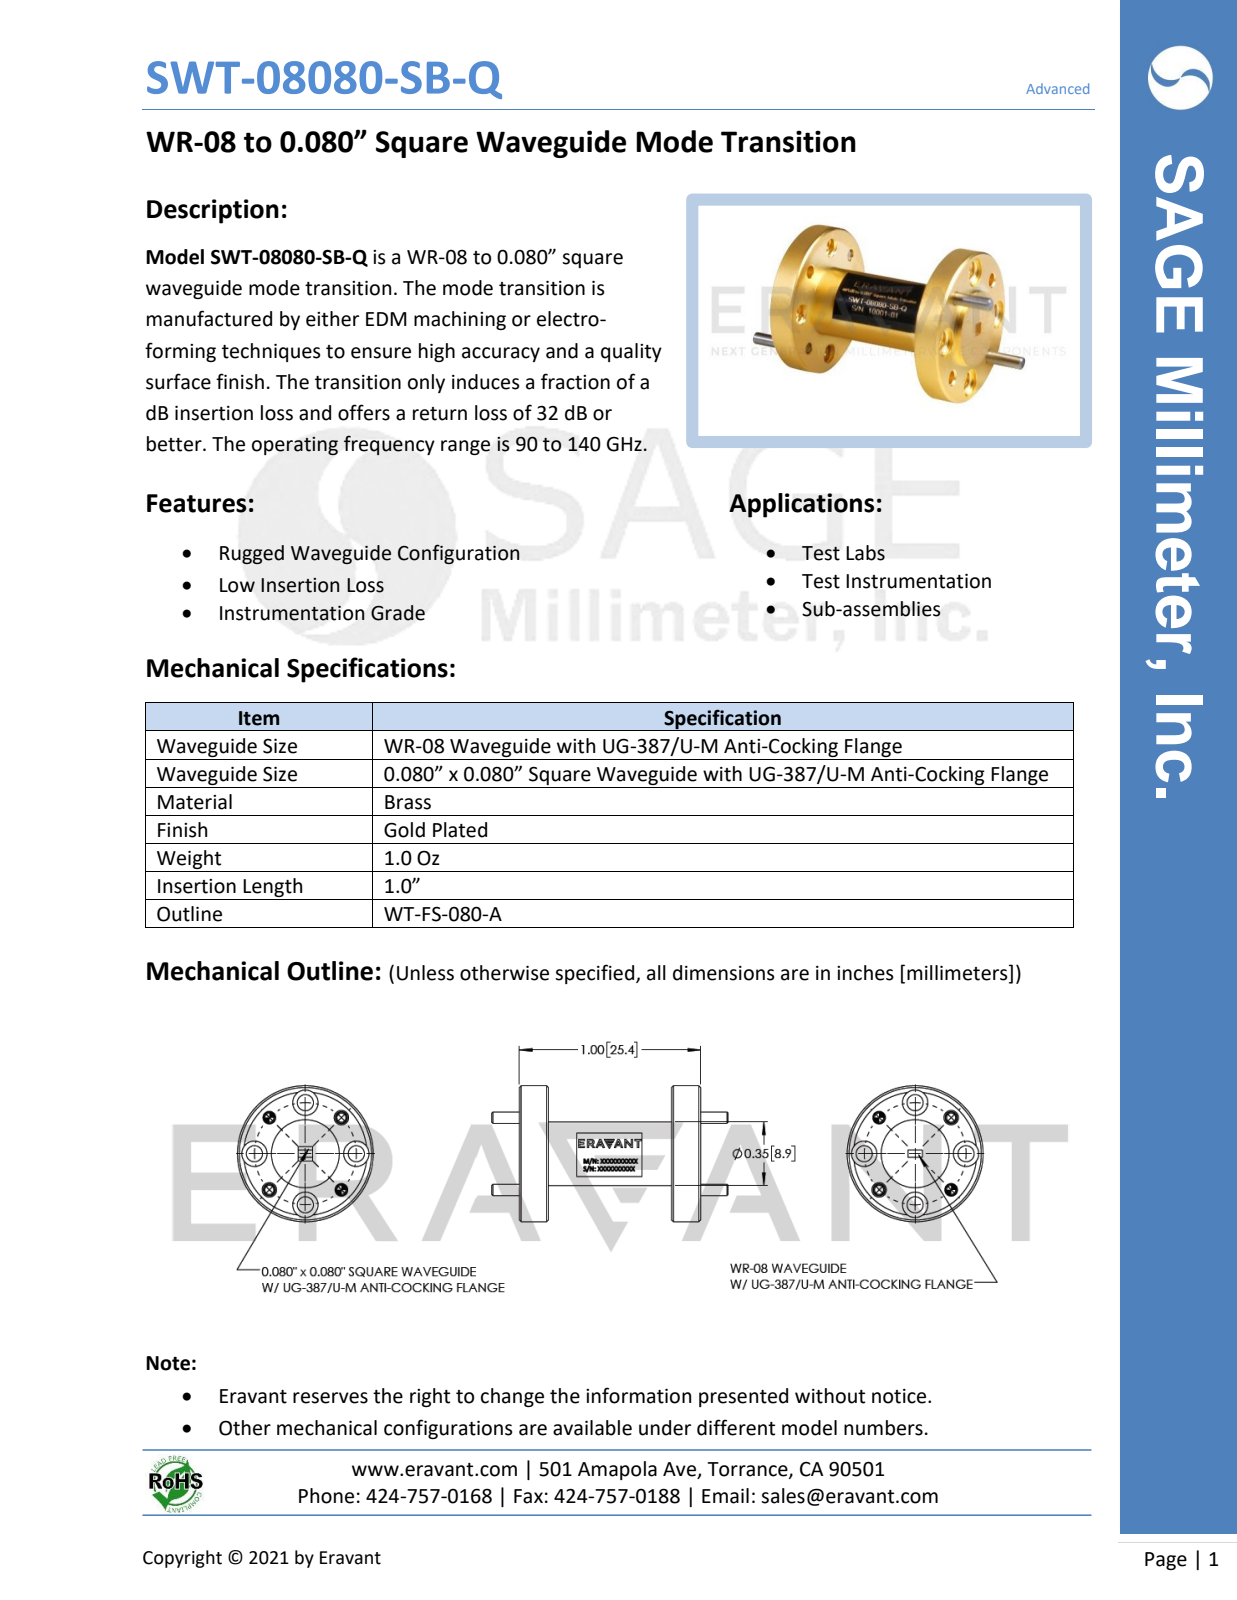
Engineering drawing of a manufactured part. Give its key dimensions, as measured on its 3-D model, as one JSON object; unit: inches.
{"part_name": "WT-FS-080-A", "step_written_by": "SolidWorks 2021 (AUTOMOTIVE_DESIGN)", "units": "inches", "bodies": {"solids": 5, "faces": 148, "planar": 34, "cylindrical": 74, "other": 40}, "overall_size": [1.305, 0.75, 0.75], "volume_in3": 0.186, "surface_area_in2": 3.858, "round_holes": [[0.061, 4], [0.067, 4], [0.089, 4], [0.14, 4], [0.68, 1]], "round_bosses_or_shafts": [[0.063, 4], [0.75, 1], [0.375, 1], [0.35, 1]], "face_to_face_distances": [0.14, 0.82, 0.02, 0.16, 0.84, 0.98, 0.68, 0.96, 1, 0.06], "hole_center_spacings": [0.215, 0.281, 0.398, 0.519, 0.562]}
